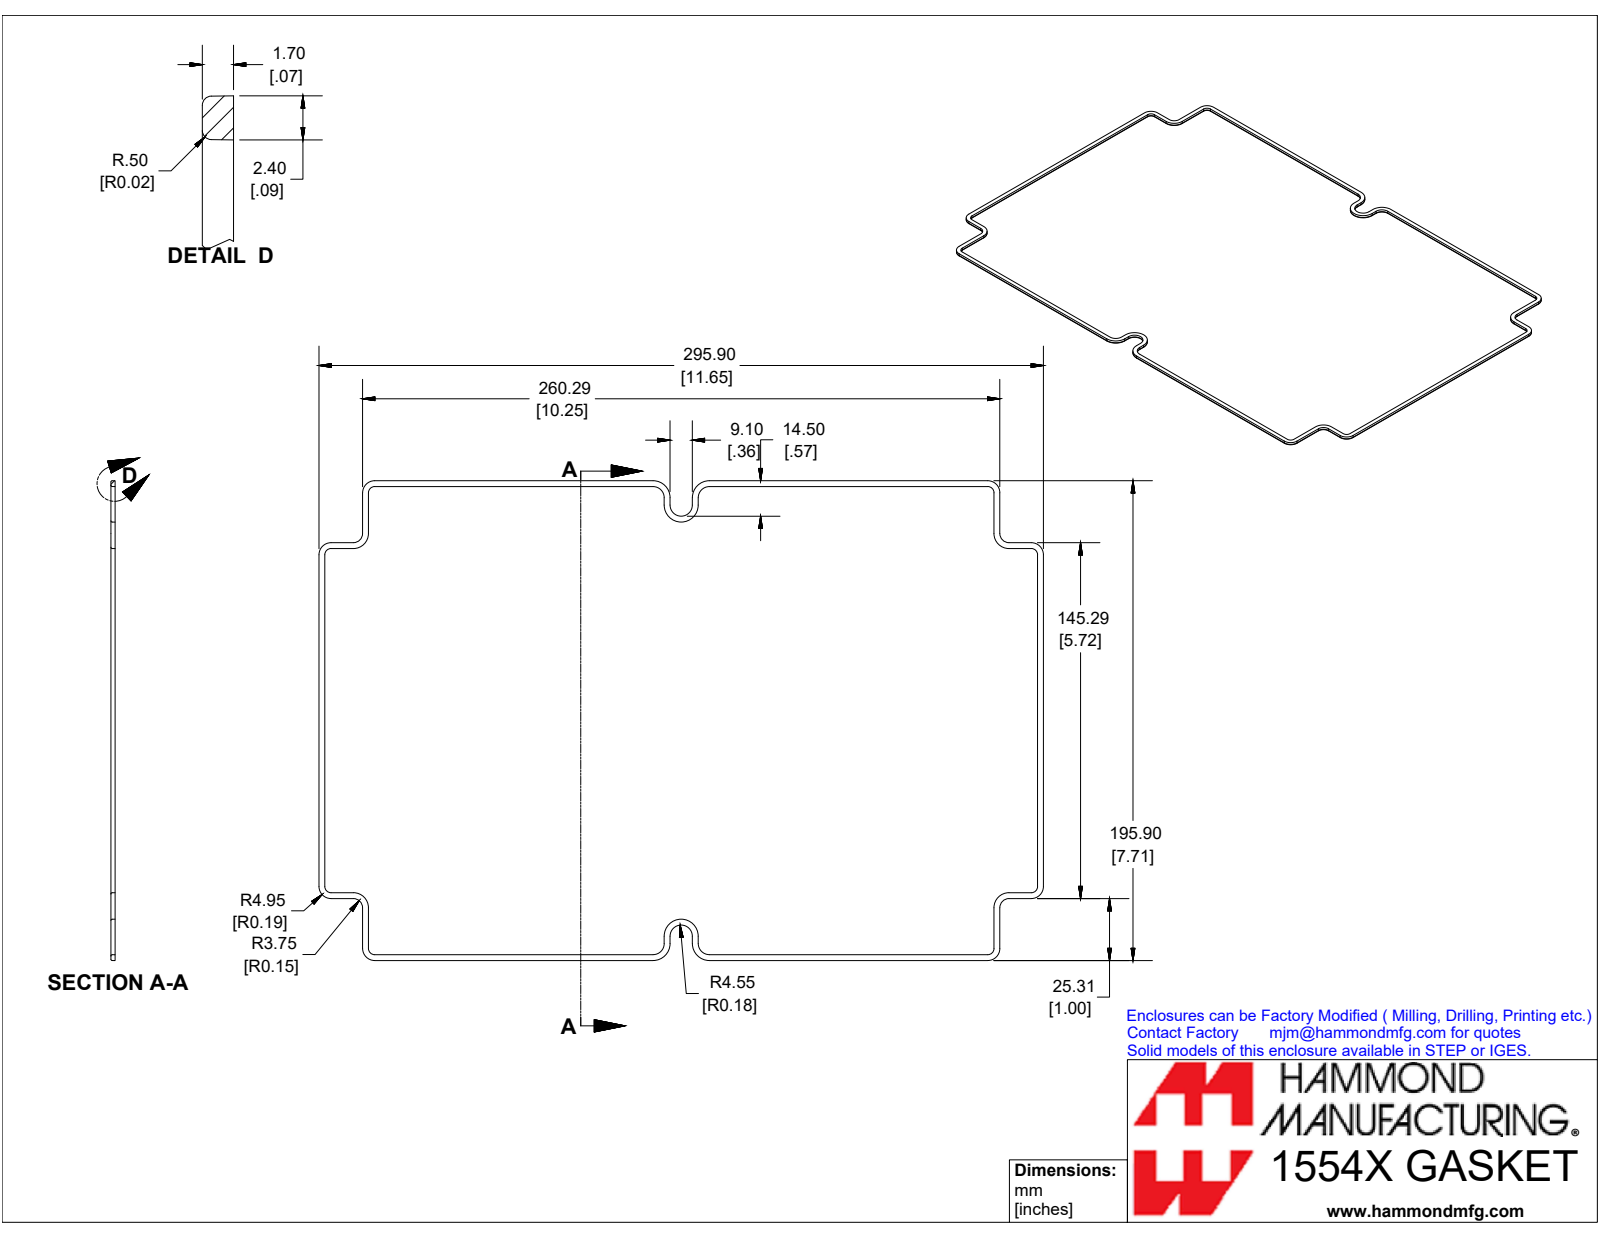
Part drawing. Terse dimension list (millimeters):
name: 1554XGASKET
written by: SolidWorks 2019 (CONFIG_CONTROL_DESIGN)
unit: mm
bodies: 1 solid, 146 faces (38 planar, 36 cylindrical, 72 other)
size: 295.9 × 195.9 × 1.7
volume: 3 900 mm³; area: 7 671 mm²
rounds: 20× R0.5
face distances: 1.7, 193.5, 293.5, 17.8, 275.7, 257.9, 168.2, 25.3, 25.3, 142.9
